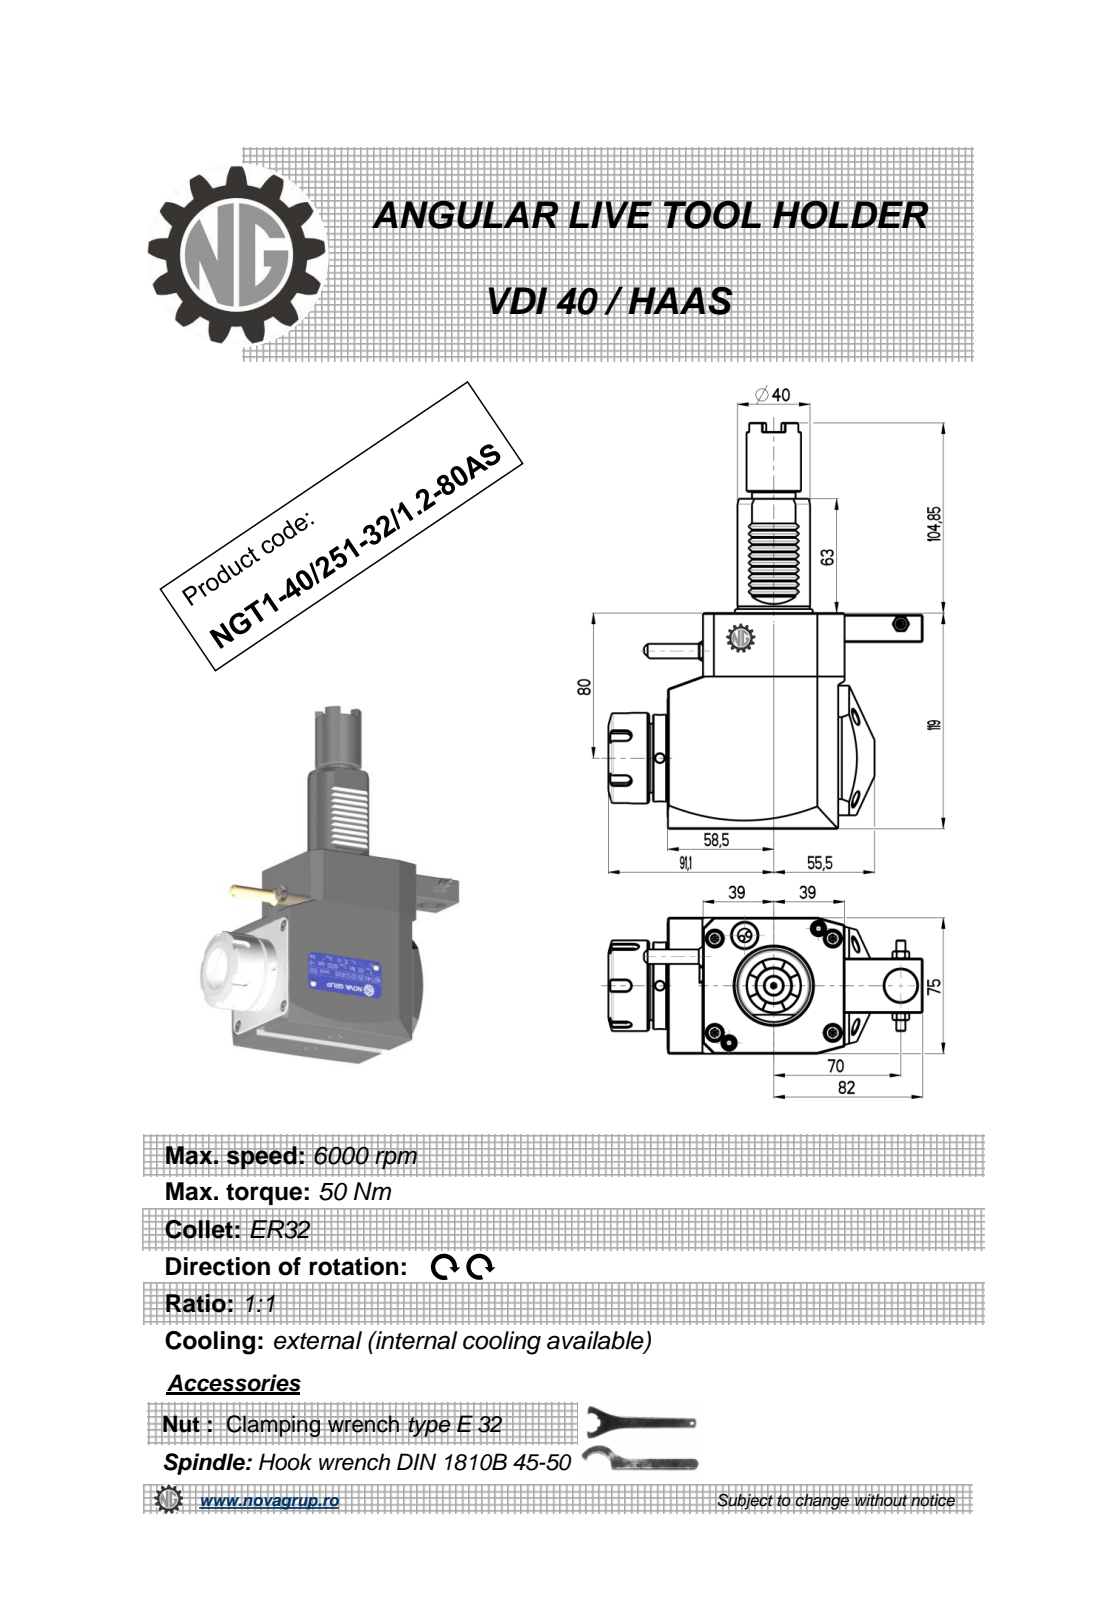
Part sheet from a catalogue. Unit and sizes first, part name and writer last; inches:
Units: inches
Overall size (bounding box): 8.813 × 6.815 × 3.016
Round holes (diameter × count): ⌀0.197 ×3, ⌀0.118 ×1, ⌀0.165 ×1, ⌀0.374 ×1, ⌀0.709 ×1, ⌀1.063 ×1
Round bosses / shafts (diameter × count): ⌀1.969 ×1, ⌀1.89 ×1, ⌀1.634 ×1, ⌀1.614 ×1, ⌀1.575 ×1, ⌀1.181 ×1, ⌀0.945 ×1, ⌀0.394 ×1
Partial cylindrical surfaces — rounded edges, fillets, slot ends (radius × count): R0.01 ×12, R0.012 ×10, R0.008 ×6, R0.118 ×5, R0.228 ×2, R0.236 ×2, R23.622 ×2, R0.02 ×1
Main face-to-face distances: 2.953, 4.685, 0.768, 3.839, 3.071, 0.039, 0.886, 0.138, 0.787, 4.488
Hole centre spacings: 0.824, 2.407, 2.854, 5.226, 5.983
Volume: 61.57 in³ · Surface area: 126.2 in²
Bodies: 1 solid, 475 faces (236 planar, 100 cylindrical, 139 other)
Part name (STEP PRODUCT): NGT1_40_251_32_1_2_80AS
STEP written by: PRO/ENGINEER BY PARAMETRIC TECHNOLOGY CORPORATION, 2010280 (CONFIG_CONTROL_DESIGN)
